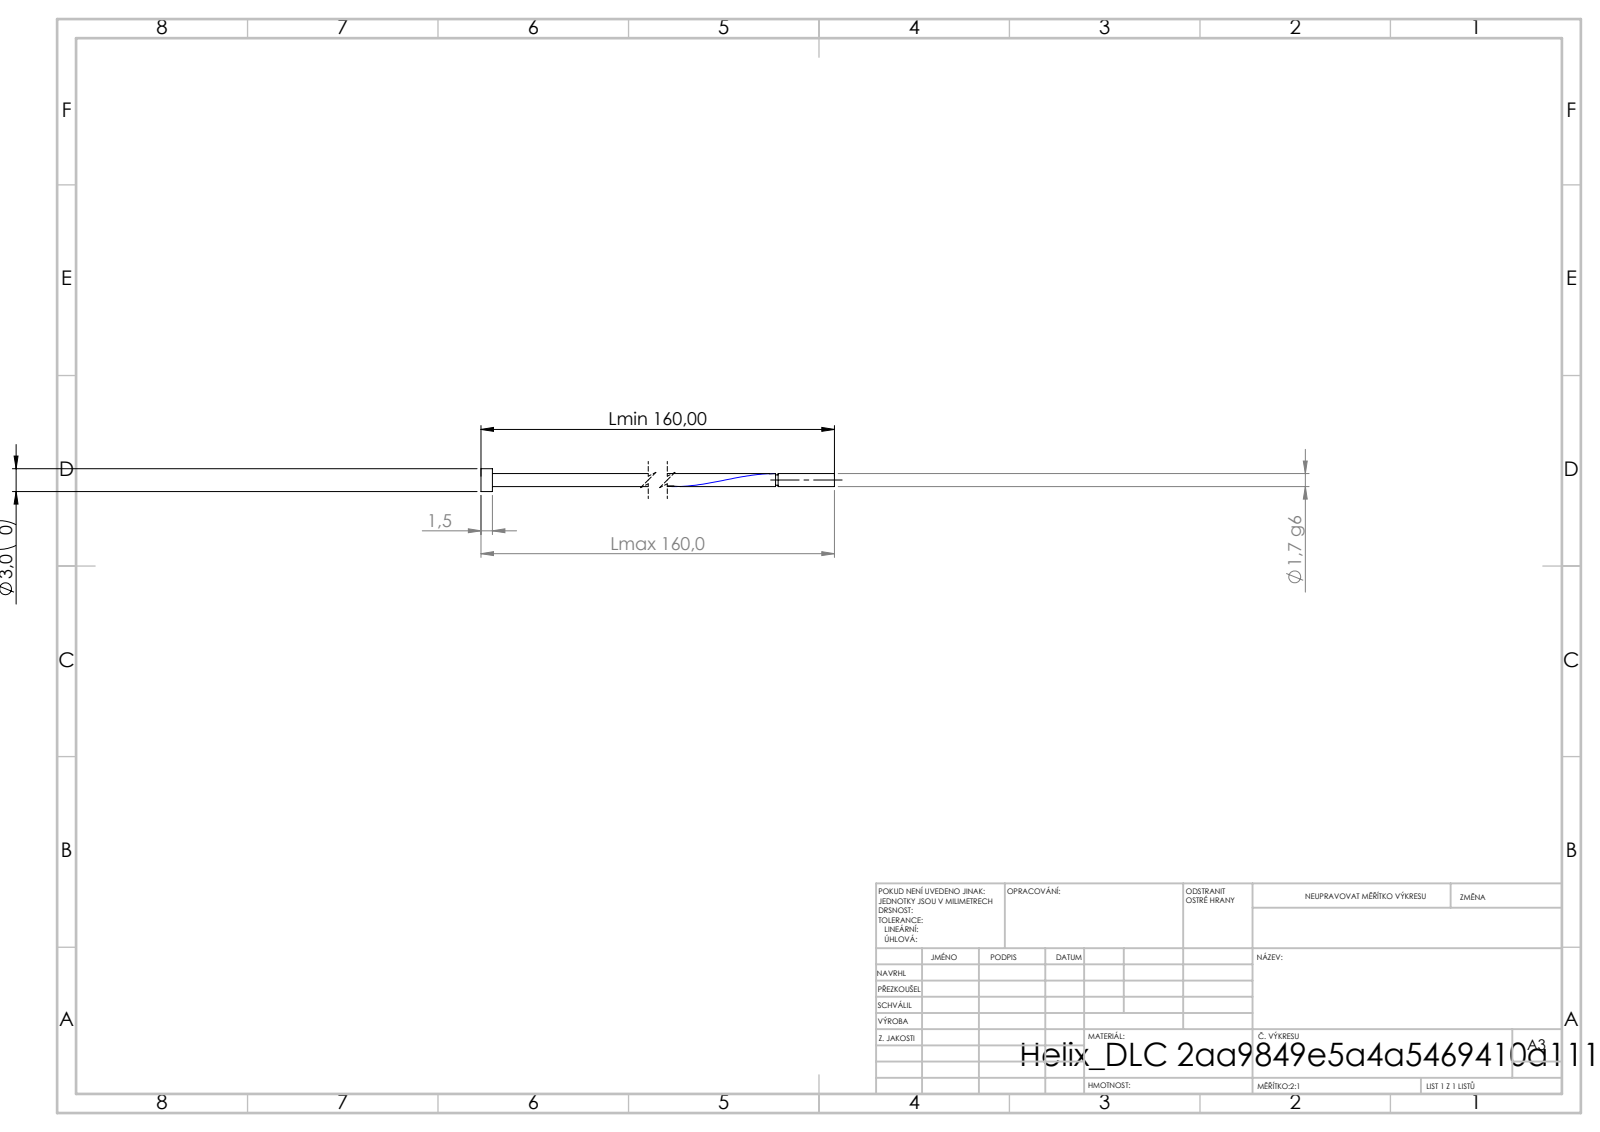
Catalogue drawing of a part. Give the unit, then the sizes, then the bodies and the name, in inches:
Units: inches
Overall size (bounding box): 6.299 × 0.118 × 0.118
Round bosses / shafts (diameter × count): ⌀0.118 ×1, ⌀0.067 ×1, ⌀0.054 ×1
Main face-to-face distances: 0.059, 6.299, 6.24, 6.009, 5.95, 0.291, 5.995, 5.936, 0.013, 0.304
Volume: 0.027 in³ · Surface area: 1.82 in²
Bodies: 1 solid, 16 faces (6 planar, 9 cylindrical, 1 other)
STEP written by: SolidWorks 2019 (CONFIG_CONTROL_DESIGN)
